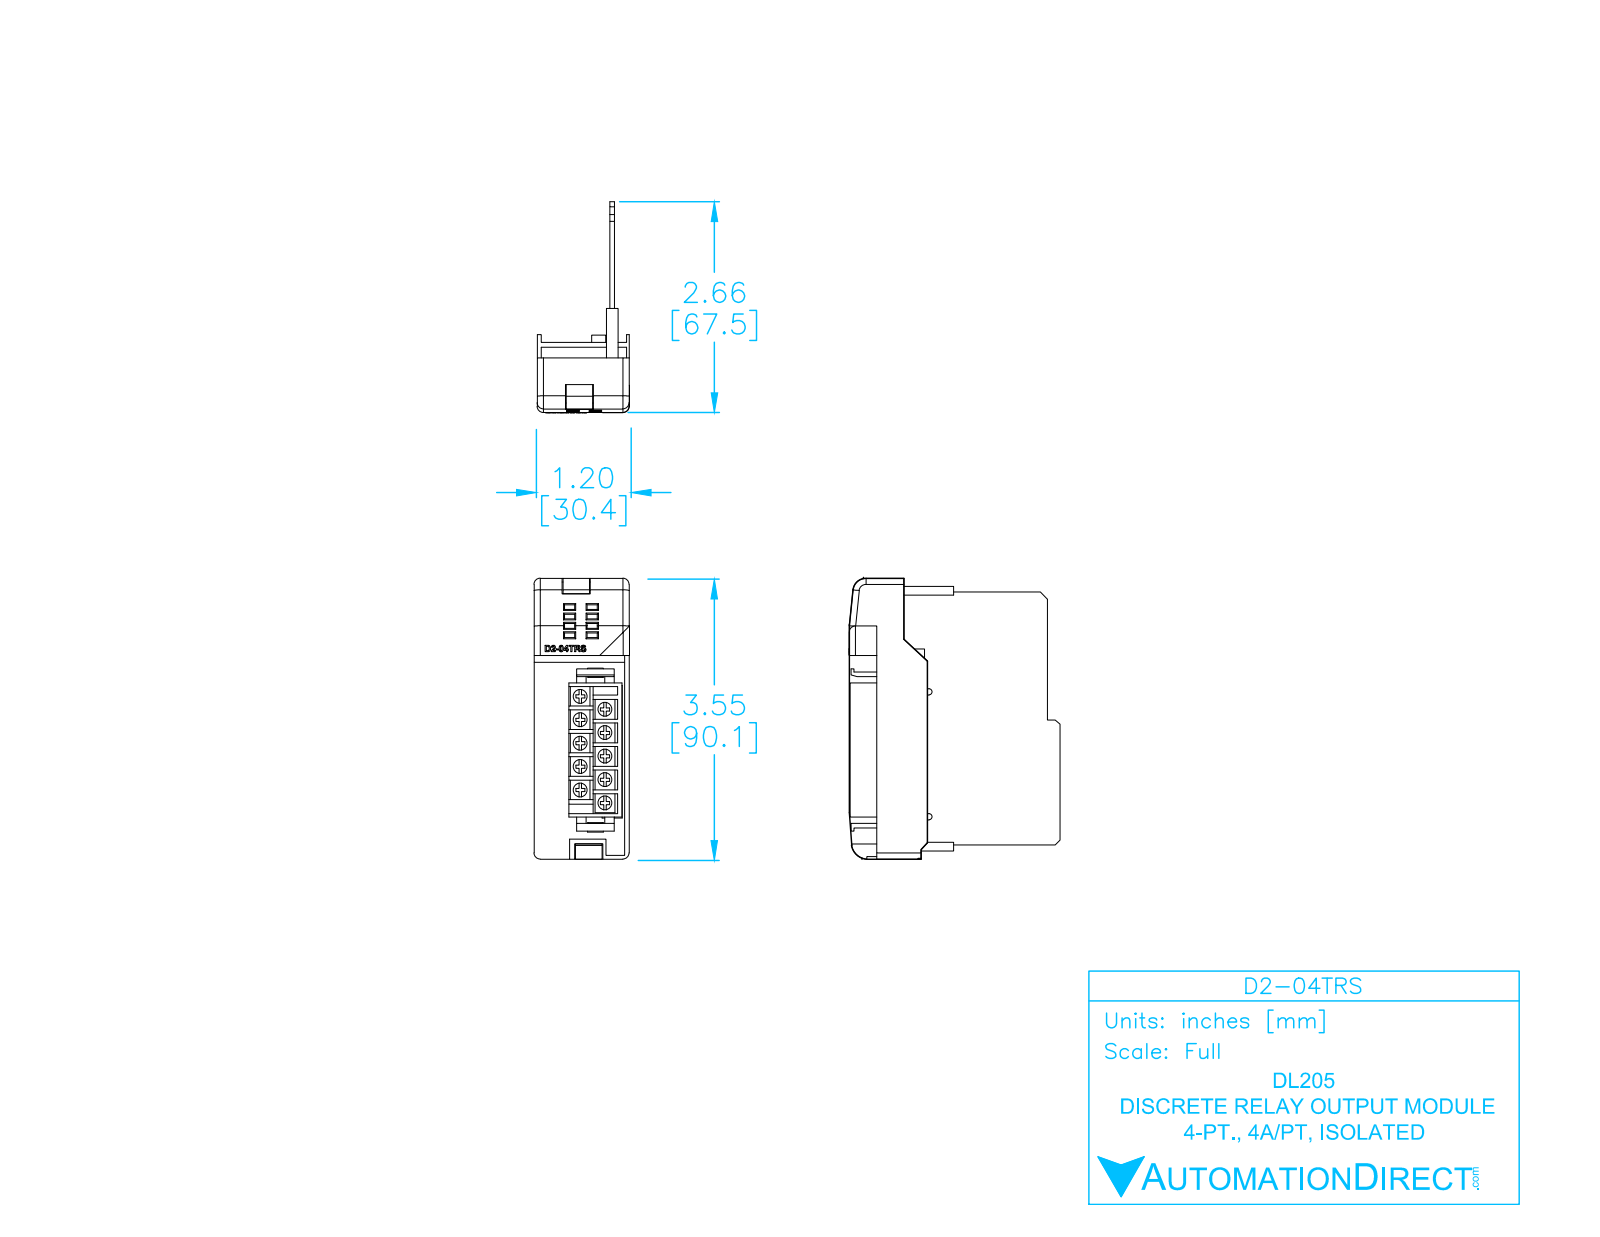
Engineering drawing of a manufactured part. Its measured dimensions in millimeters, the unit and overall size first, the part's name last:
Units: millimetres
Overall size (bounding box): 90 × 67.61 × 30.55
Round bosses / shafts (diameter × count): ⌀4.5 ×10
Partial cylindrical surfaces — rounded edges, fillets, slot ends (radius × count): R0.35 ×16, R2 ×9, R0.25 ×2, R1 ×2, R1.25 ×2, R4.12 ×1, R5.39 ×1
Main face-to-face distances: 1.5, 4.72, 6.22, 2.37, 3.87, 2.35, 3.22, 0.85, 8.14, 24.28
Volume: 25 374 mm³ · Surface area: 28 533 mm²
Bodies: 6 solids, 586 faces (415 planar, 75 cylindrical, 96 other)
Part name (STEP PRODUCT): D2-04TRS_ModuleCase_light_NEW
STEP written by: SolidWorks 2009 (AUTOMOTIVE_DESIGN)
